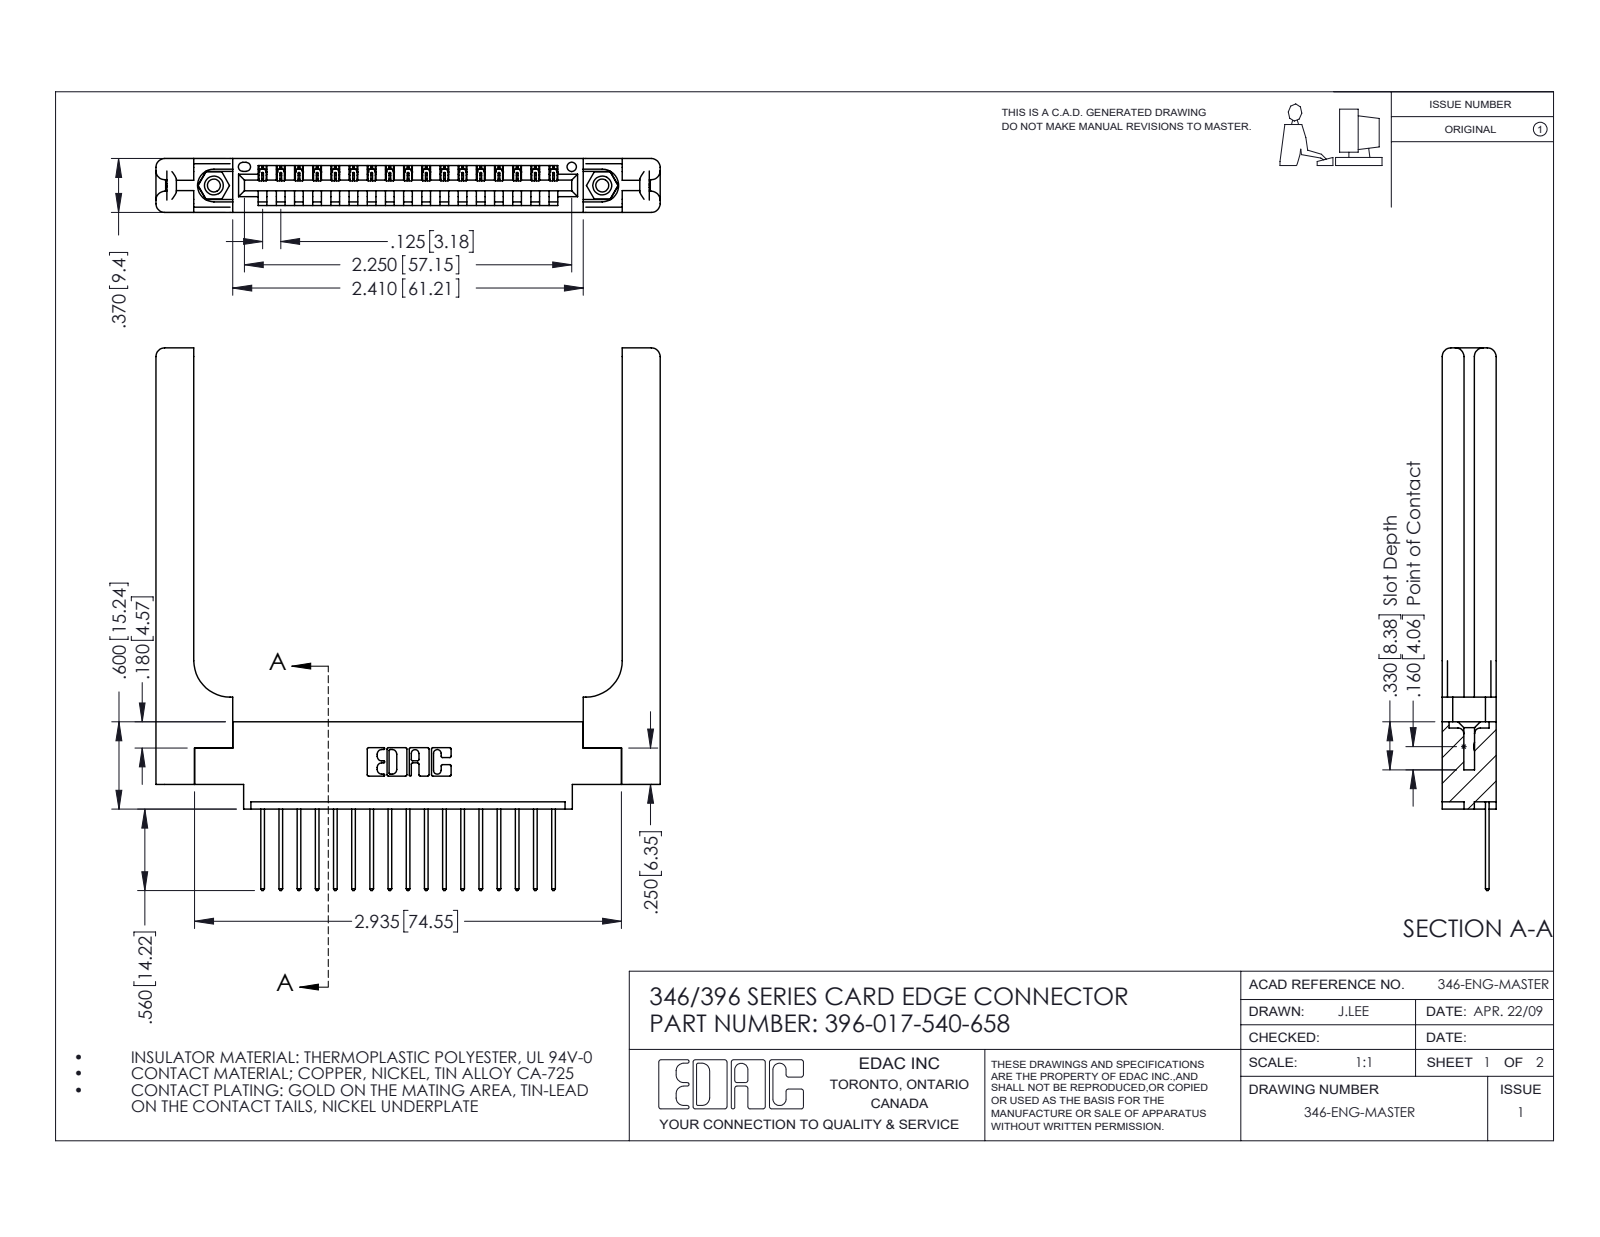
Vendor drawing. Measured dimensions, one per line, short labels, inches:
name: 345-292-001_345-293-140; 346 Part_0.170 Offset - 0.156 Dia-TH; 346-220-058_345-220-058; 345-250-001_345-250-001-102 (+1 more)
written by: SolidWorks 2016 (CONFIG_CONTROL_DESIGN)
unit: in
bodies: 22 solids, 1368 faces (908 planar, 400 cylindrical, 60 other)
size: 3.73 × 3.466 × 0.37
volume: 0.955 in³; area: 23.84 in²
holes: 2× ⌀0.089, 2× ⌀0.125, 2× ⌀0.156, 1× ⌀0.064
bosses: 2× ⌀0.155
rounds: 34× R0.006, 34× R0.01, 22× R0.01, 16× R0.06, 6× R0.007, 6× R0.031, 3× R0.026, 2× R0.03
face distances: 0.37, 0.072, 0.15, 0.148, 0.048, 0.322, 0.25, 0.102, 0.22, 0.173
hole spacings: 0.246, 2.463, 2.67
